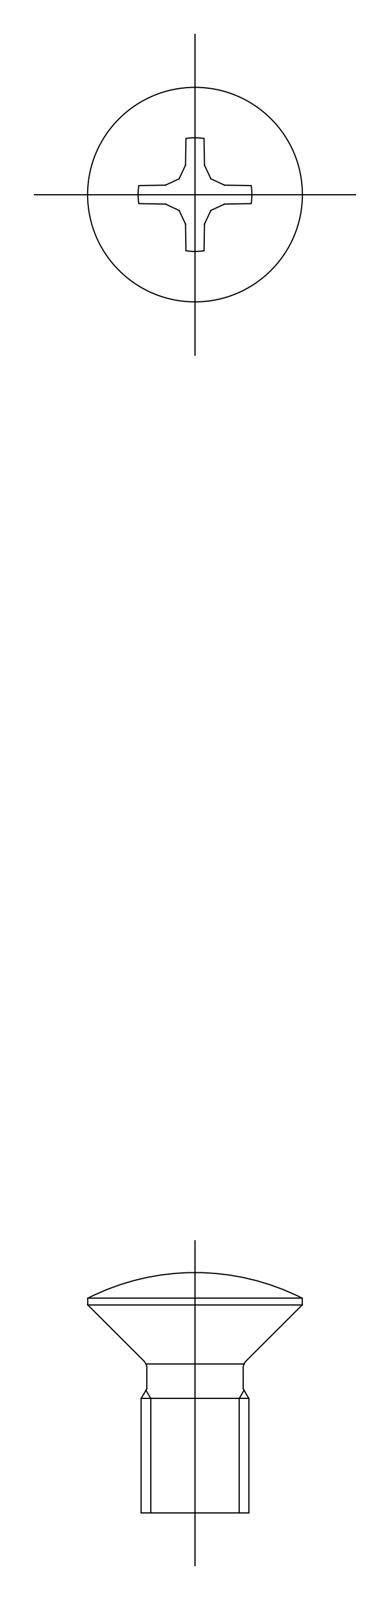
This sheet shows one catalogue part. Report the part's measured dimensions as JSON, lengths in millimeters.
{"part_name": "screw", "step_written_by": "CADfix (AUTOMOTIVE_DESIGN)", "units": "millimeters", "bodies": {"solids": 1, "faces": 27, "planar": 0, "cylindrical": 0, "other": 27}, "overall_size": [11.18, 10, 10], "volume_mm3": 313, "surface_area_mm2": 330}
